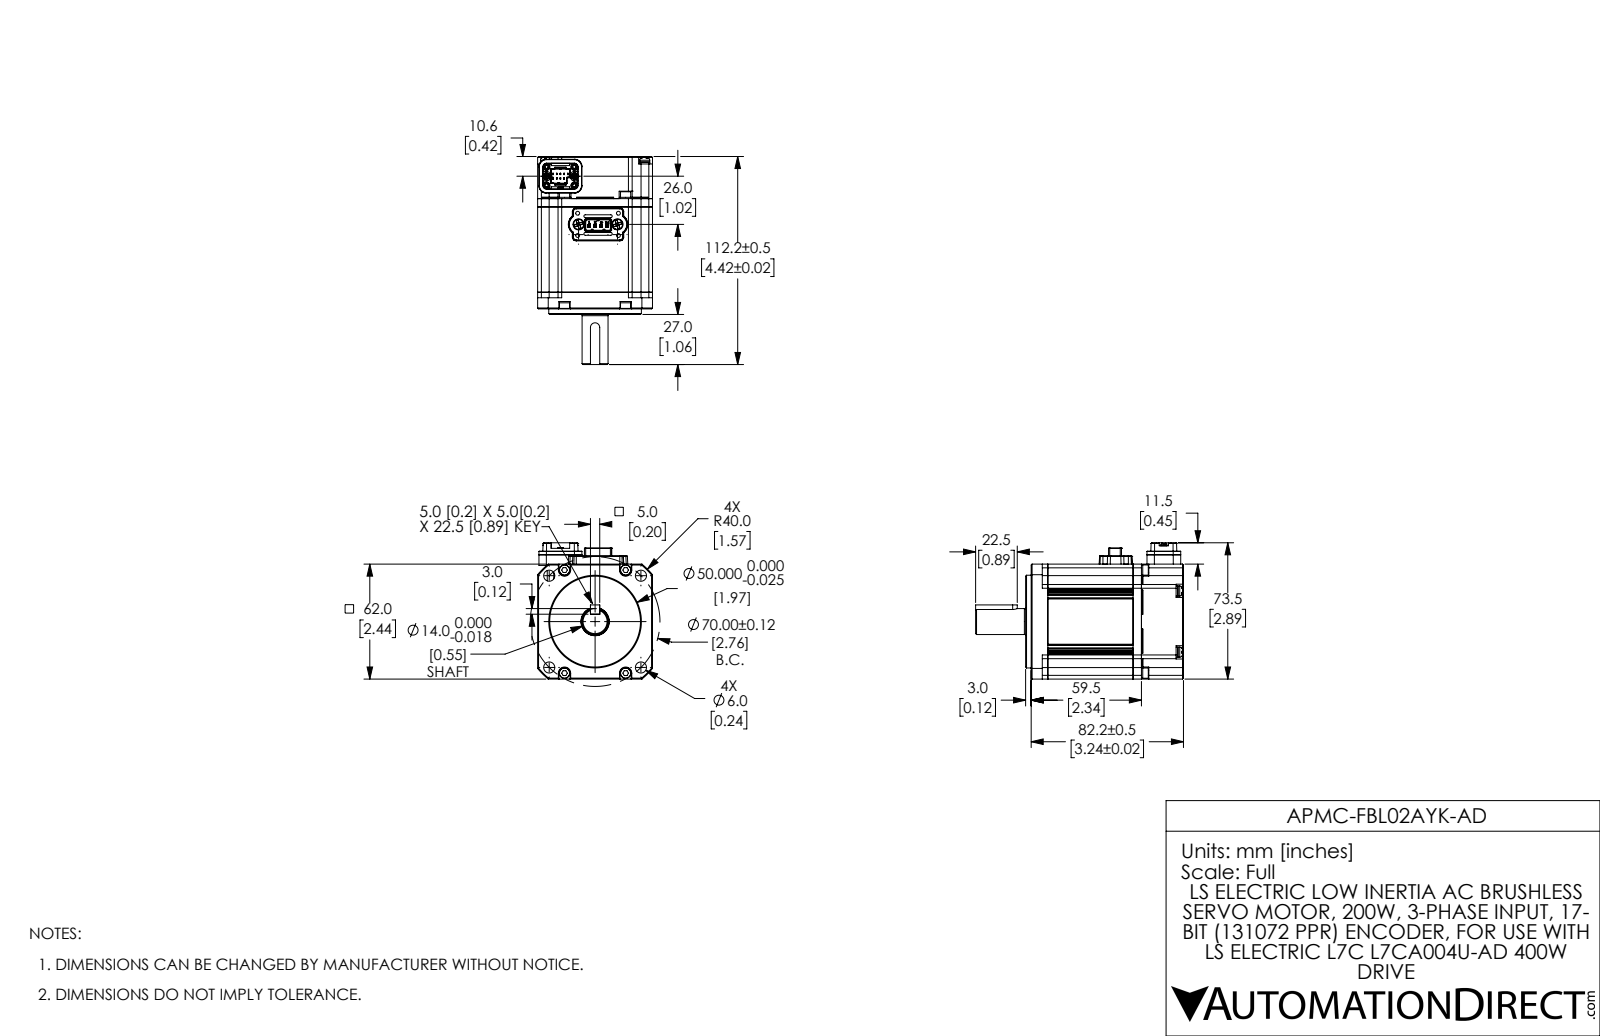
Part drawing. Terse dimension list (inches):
name: APMC-FBL02AYK-AD
written by: SolidWorks 2017 (AUTOMOTIVE_DESIGN)
unit: in
bodies: 45 solids, 1851 faces (1196 planar, 478 cylindrical, 177 other)
size: 4.417 × 2.894 × 2.441
volume: 17.8 in³; area: 109.7 in²
holes: 10× ⌀0.083, 10× ⌀0.118, 8× ⌀0.138, 6× ⌀0.063, 6× ⌀0.236, 4× ⌀0.122, 1× ⌀0.13, 1× ⌀0.134, 1× ⌀0.602
bosses: 6× ⌀0.213, 4× ⌀0.22, 4× ⌀0.217, 2× ⌀0.087, 1× ⌀1.969, 1× ⌀0.591, 1× ⌀0.583, 1× ⌀0.551
rounds: 20× R0.008, 20× R0.012, 12× R0.118, 10× R0.039, 9× R0.006, 8× R0.079, 7× R0.018, 6× R0.004
face distances: 0.177, 0.028, 0.205, 1.811, 1.988, 2.016, 2.441, 0.354, 0.118, 0.866
hole spacings: 0.197, 0.237, 0.335, 0.346, 0.602, 0.63, 0.879, 1.239
